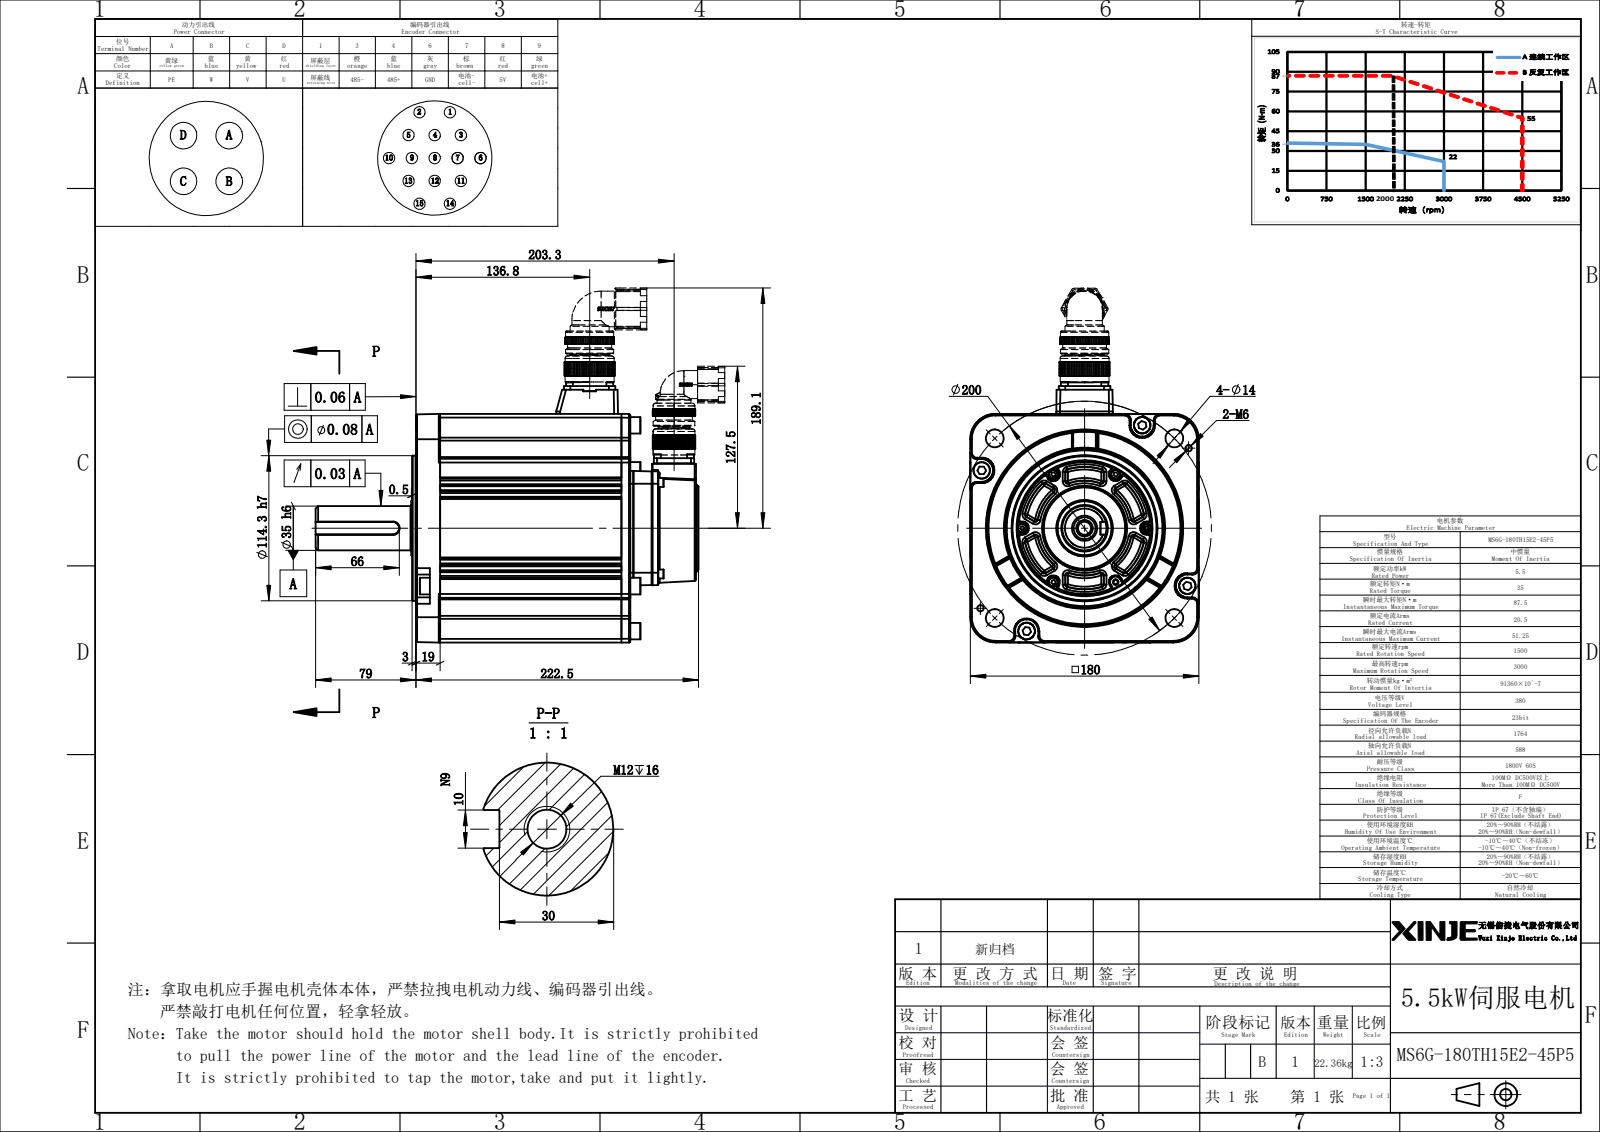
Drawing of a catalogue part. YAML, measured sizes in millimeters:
part_name: "MS6G-180TH15E2-45P5"
step_written_by: "SolidWorks 2022 (CONFIG_CONTROL_DESIGN)"
units: millimeters
bodies: {solids: 42, faces: 3496, planar: 1364, cylindrical: 882, other: 1250}
overall_size: [301.5, 221.1, 180]
volume: 5186000
surface_area: 478108
round_holes:
  - {diameter: 1.5, count: 15}
  - {diameter: 4.5, count: 10}
  - {diameter: 3.2, count: 6}
  - {diameter: 6.8, count: 6}
  - {diameter: 2.5, count: 5}
  - {diameter: 1.8, count: 4}
  - {diameter: 3.3, count: 4}
  - {diameter: 3.6, count: 4}
  - {diameter: 3.7, count: 4}
  - {diameter: 4, count: 4}
  - {diameter: 5.45, count: 4}
  - {diameter: 6.2, count: 4}
round_bosses_or_shafts:
  - {diameter: 2.5, count: 15}
  - {diameter: 2, count: 15}
  - {diameter: 7, count: 10}
  - {diameter: 4, count: 10}
  - {diameter: 3, count: 9}
  - {diameter: 5.5, count: 8}
  - {diameter: 13, count: 4}
  - {diameter: 8, count: 4}
partial_cylinders:
  - {radius: 1, count: 86}
  - {radius: 3, count: 39}
  - {radius: 0.2, count: 17}
  - {radius: 2, count: 16}
  - {radius: 5, count: 13}
  - {radius: 7.72, count: 13}
  - {radius: 2.5, count: 12}
  - {radius: 0.8, count: 6}
face_to_face_distances: [142.8, 7, 180, 161.8, 149.8, 2.7, 5, 9.7, 152.5, 9]
hole_center_spacings: [49, 16.04, 112.25, 21.08, 3.6, 7.2, 3.83, 3.86]
